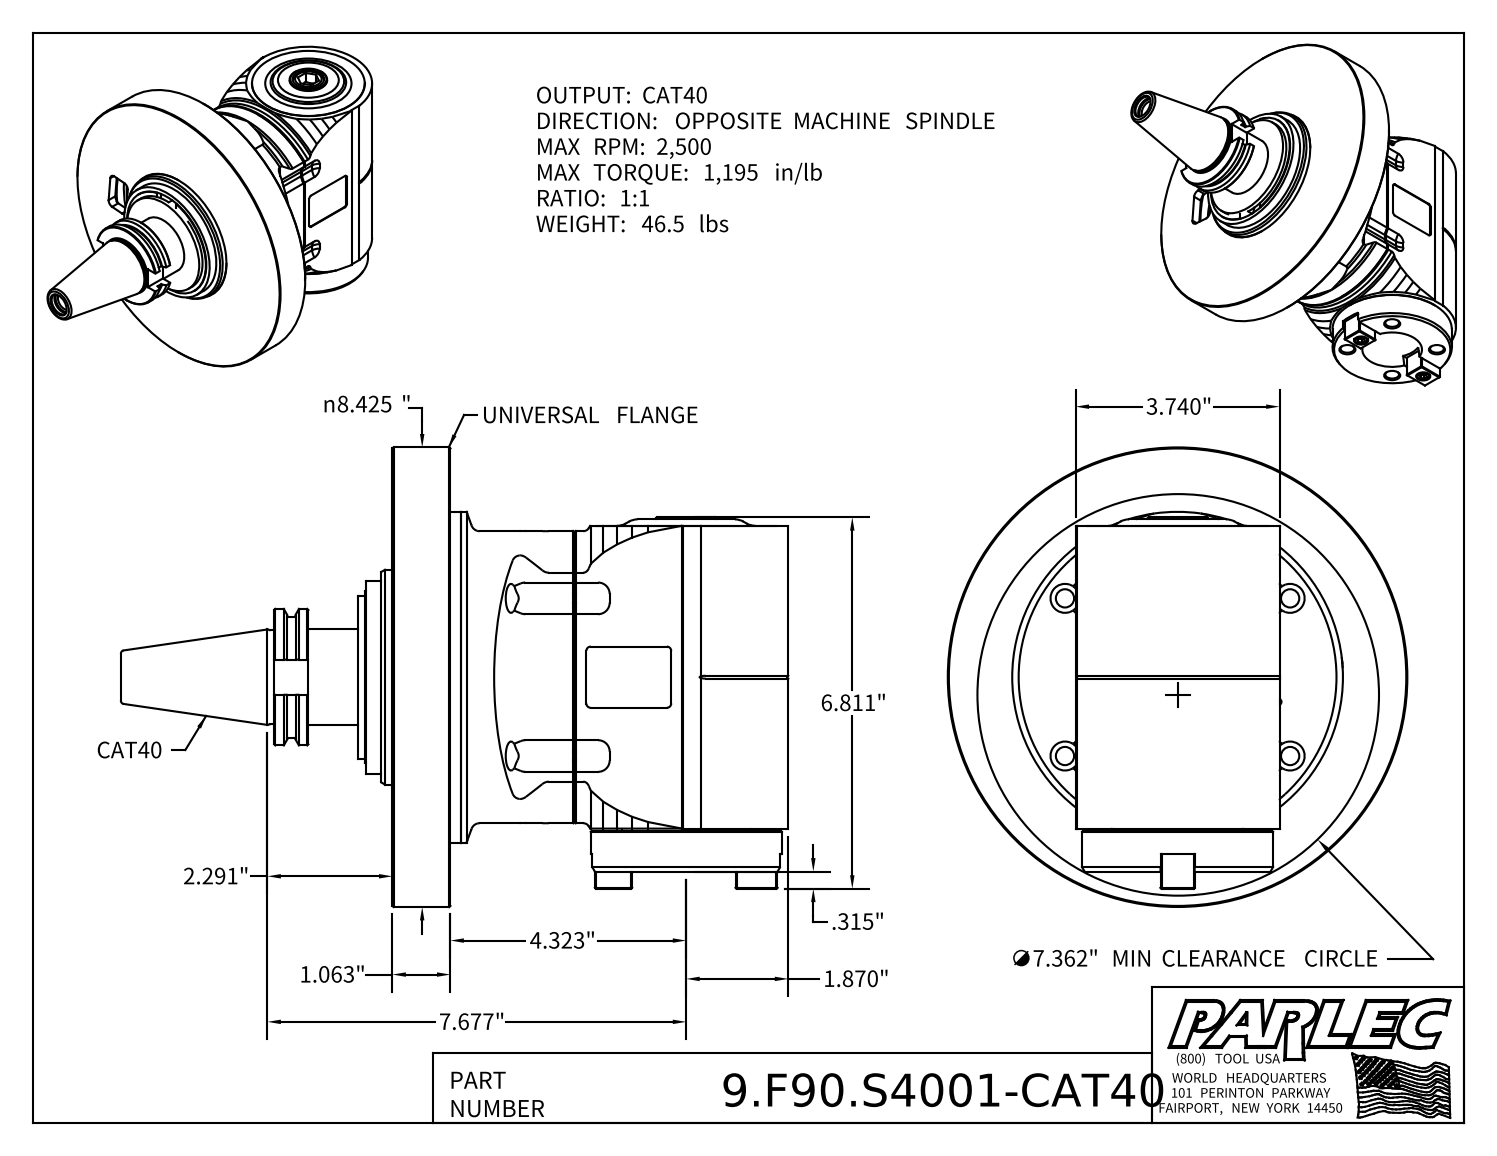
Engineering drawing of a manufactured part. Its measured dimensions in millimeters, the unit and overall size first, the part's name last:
Units: millimetres
Overall size (bounding box): 310.7 × 214 × 214
Round holes (diameter × count): ⌀8.5 ×4, ⌀10.3 ×4, ⌀13.5 ×4, ⌀10.5 ×2, ⌀9.5 ×1, ⌀12.5 ×1, ⌀13.4 ×1, ⌀16.3 ×1, ⌀16.5 ×1, ⌀16.8 ×1, ⌀20 ×1, ⌀23.5 ×1
Round bosses / shafts (diameter × count): ⌀10 ×2, ⌀2.5 ×2, ⌀214 ×1, ⌀154 ×1, ⌀117.7 ×1, ⌀111.7 ×1, ⌀90 ×1, ⌀88.9 ×1
Partial cylindrical surfaces — rounded edges, fillets, slot ends (radius × count): R2 ×12, R7 ×12, R4 ×8, R47.5 ×1, R68 ×1, R74 ×1
Main face-to-face distances: 27, 5, 34.7, 10.2, 16.8, 22, 5.2, 29.5, 39.7, 12.7
Hole centre spacings: 25.3, 33.4, 47.2, 61.1, 64, 32.7, 66.7, 73.4
Volume: 3 230 000 mm³ · Surface area: 300 200 mm²
Bodies: 4 solids, 468 faces (196 planar, 122 cylindrical, 150 other)
Part name (STEP PRODUCT): 9.F90.S4001-CAT40; 9_F90_S4001; 9_SK_44_2 (Cat40, MTC); 9_FL_F90T3 (MTC, Universal Flange, Type 3)
STEP written by: Autodesk Inventor 2022 (AUTOMOTIVE_DESIGN)
